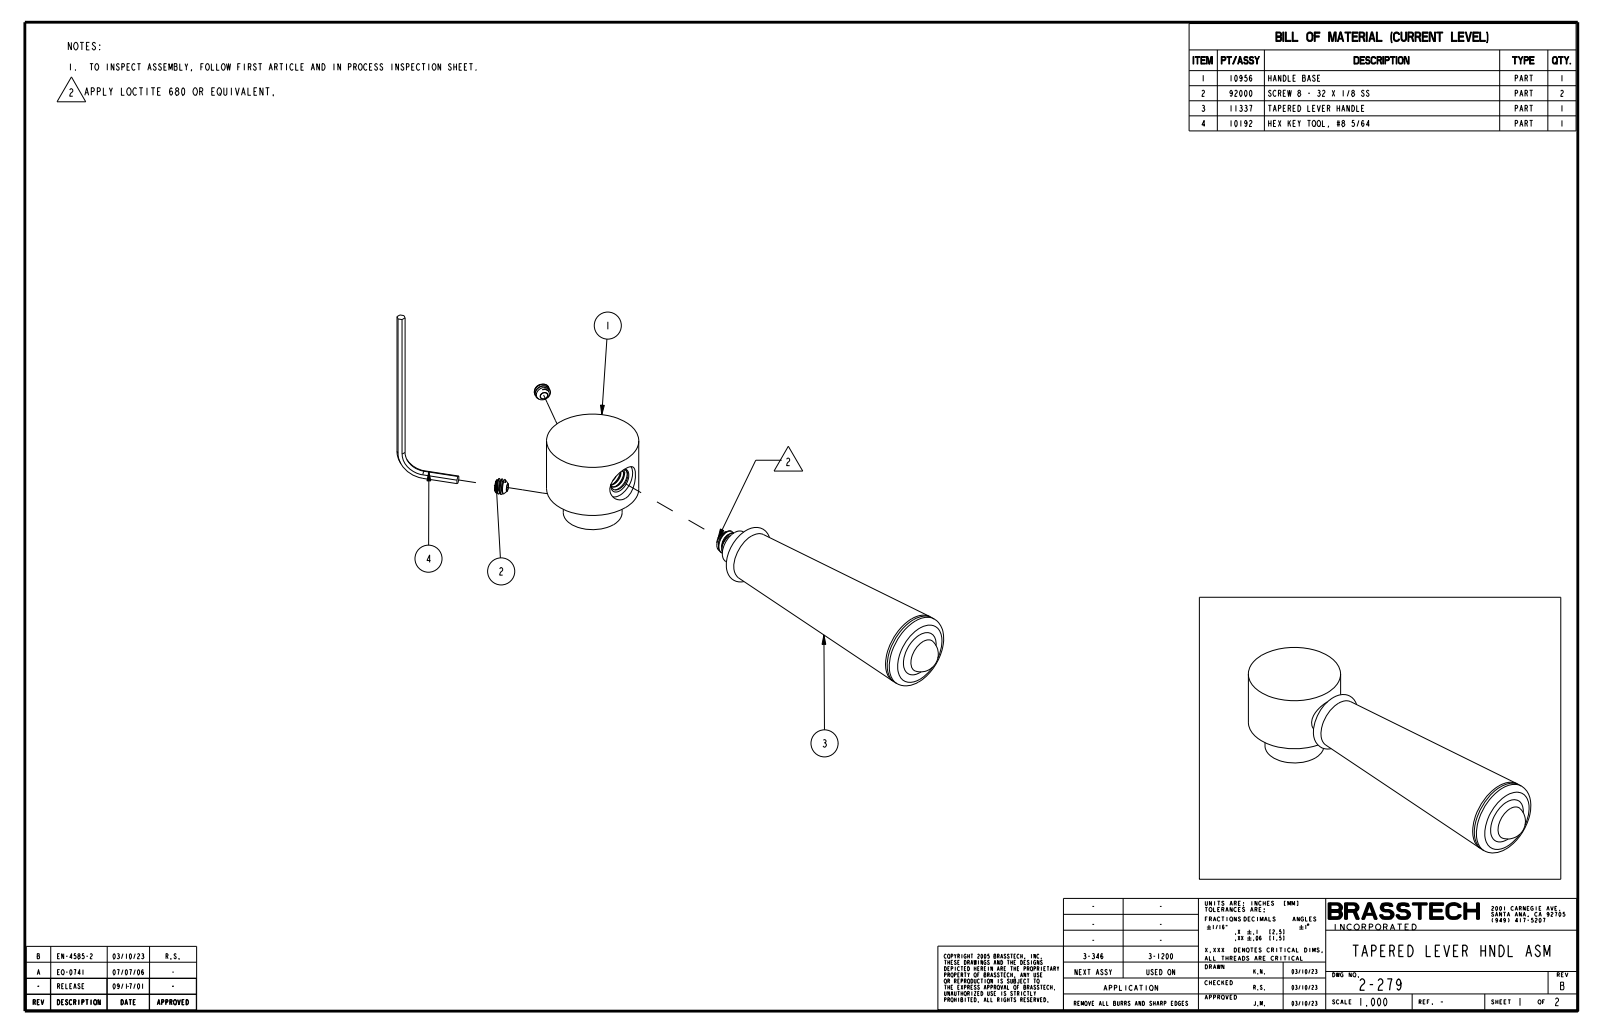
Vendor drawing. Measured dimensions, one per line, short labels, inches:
name: 10956; 92000; 11337; 2-279_ASM
written by: CREO PARAMETRIC BY PTC INC, 2018400 (CONFIG_CONTROL_DESIGN)
unit: in
bodies: 4 solids, 326 faces (107 planar, 91 cylindrical, 128 other)
size: 3.883 × 1.019 × 0.98
volume: 1.448 in³; area: 21.97 in²
holes: 2× ⌀0.136, 1× ⌀0.201, 1× ⌀0.339, 1× ⌀0.385
bosses: 2× ⌀0.164, 1× ⌀0.98, 1× ⌀0.792, 1× ⌀0.625, 1× ⌀0.365, 1× ⌀0.25, 1× ⌀0.18
rounds: 1× R0.187
face distances: 0.152, 0.31, 2.785, 0.08, 0.162, 2.623, 0.115, 0.195, 0.18, 0.342
